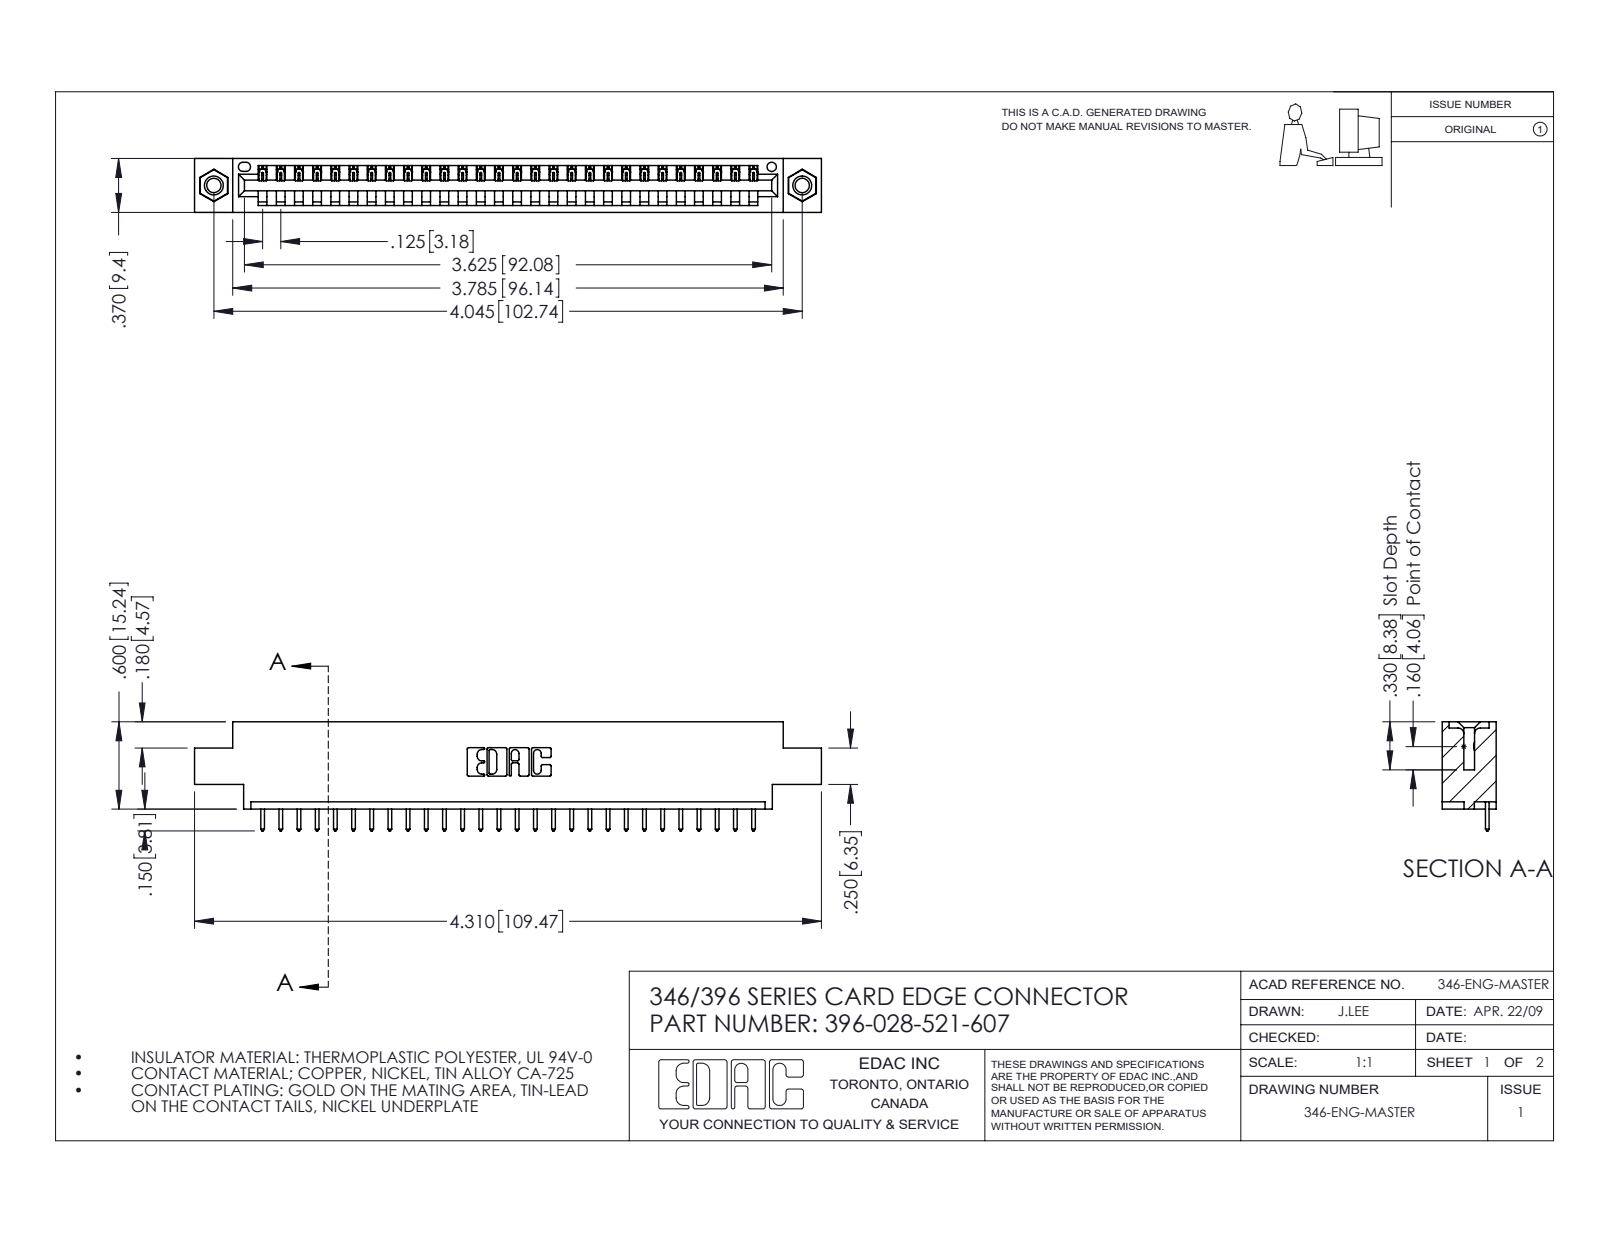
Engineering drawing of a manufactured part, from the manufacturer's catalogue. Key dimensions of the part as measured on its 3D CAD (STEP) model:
Part name (STEP PRODUCT): 396-028-521-607; 345-292-001_345-293-121; 345-250-001_345-250-005-103; 346 Part_0.170 Offset - 0.156 Dia-TI
STEP written by: SolidWorks 2016 (CONFIG_CONTROL_DESIGN)
Units: inches
Bodies: 31 solids, 1810 faces (1232 planar, 562 cylindrical, 16 other)
Overall size (bounding box): 4.31 × 0.75 × 0.37
Volume: 0.618 in³ · Surface area: 19.21 in²
Round holes (diameter × count): ⌀0.098 ×2, ⌀0.125 ×2, ⌀0.156 ×2, ⌀0.064 ×1
Round bosses / shafts (diameter × count): ⌀0.155 ×2
Partial cylindrical surfaces — rounded edges, fillets, slot ends (radius × count): R0.006 ×56, R0.01 ×56, R0.01 ×22, R0.007 ×6, R0.031 ×6, R0.026 ×3, R0.031 ×2, R0.04 ×2
Main face-to-face distances: 0.048, 0.322, 0.37, 0.25, 0.072, 0.298, 0.025, 0.222, 0.148, 0.1
Hole centre spacings: 0.246, 3.837, 4.045
